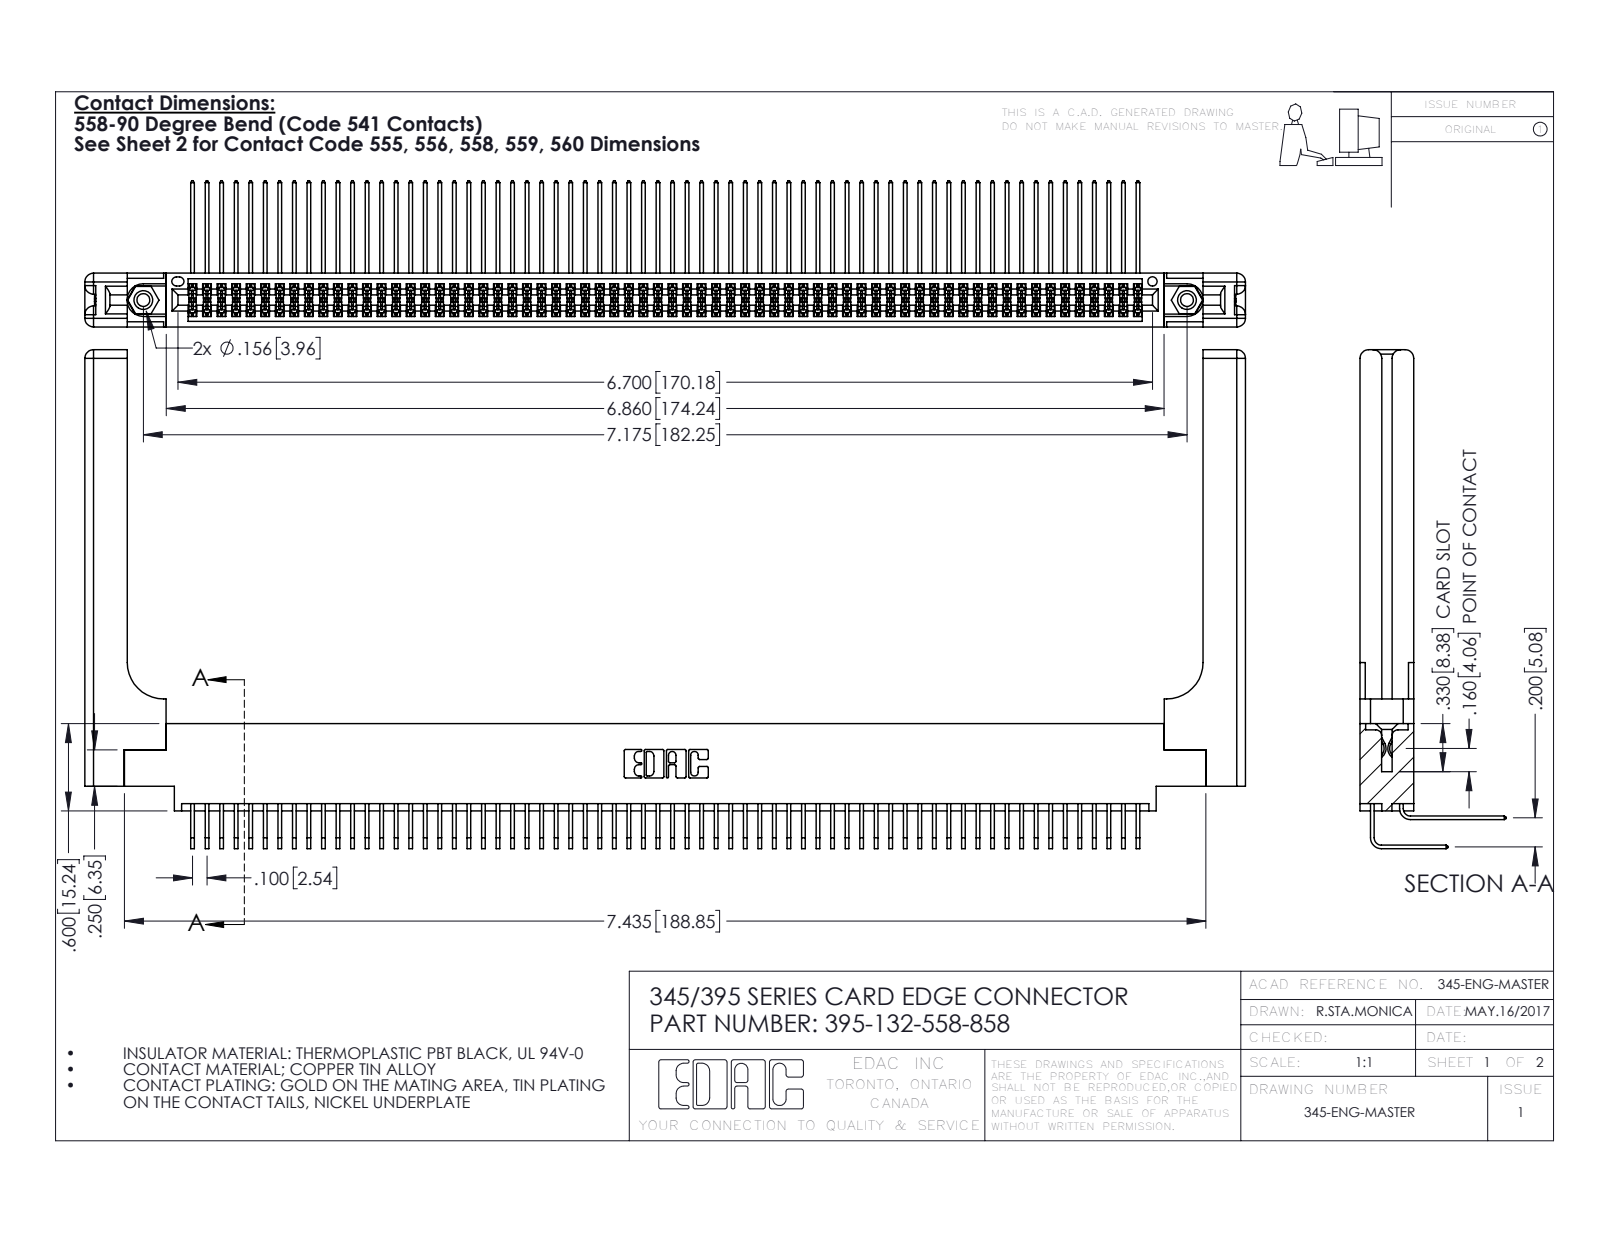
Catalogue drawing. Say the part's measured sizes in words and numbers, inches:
The part is named "345-220-058_345-220-058; 345-292-001_558 Tail - 2; 345-250-001_345-250-001-102; 345 Part_0.170 Offset - 0.156 Dia-TH (+2 more)". Its 3-D file was written by "SolidWorks 2016 (CONFIG_CONTROL_DESIGN)". It is 137 solids with 7250 faces: 4852 planar, 2338 cylindrical and 60 other. Overall it measures 7.979 by 3.429 by 1.005 inches. Its volume is 1.772 cubic inches and its surface area 61.44 square inches. Round holes: 2 of diameter 0.089, 2 of diameter 0.125, 2 of diameter 0.156, 1 of diameter 0.064. Round bosses or shafts: 2 of diameter 0.155. Partial cylindrical surfaces (rounded edges, fillets, slot ends): 199 of radius 0.006, 22 of radius 0.01, 16 of radius 0.06, 6 of radius 0.007, 6 of radius 0.031, 3 of radius 0.026, 2 of radius 0.014, 2 of radius 0.019. The main face-to-face distances are 0.072, 0.298, 0.37, 0.2, 0.098, 0.272, 0.025, 0.225, 0.175, 0.025. The hole center spacings are 0.27, 6.939, 7.175.
